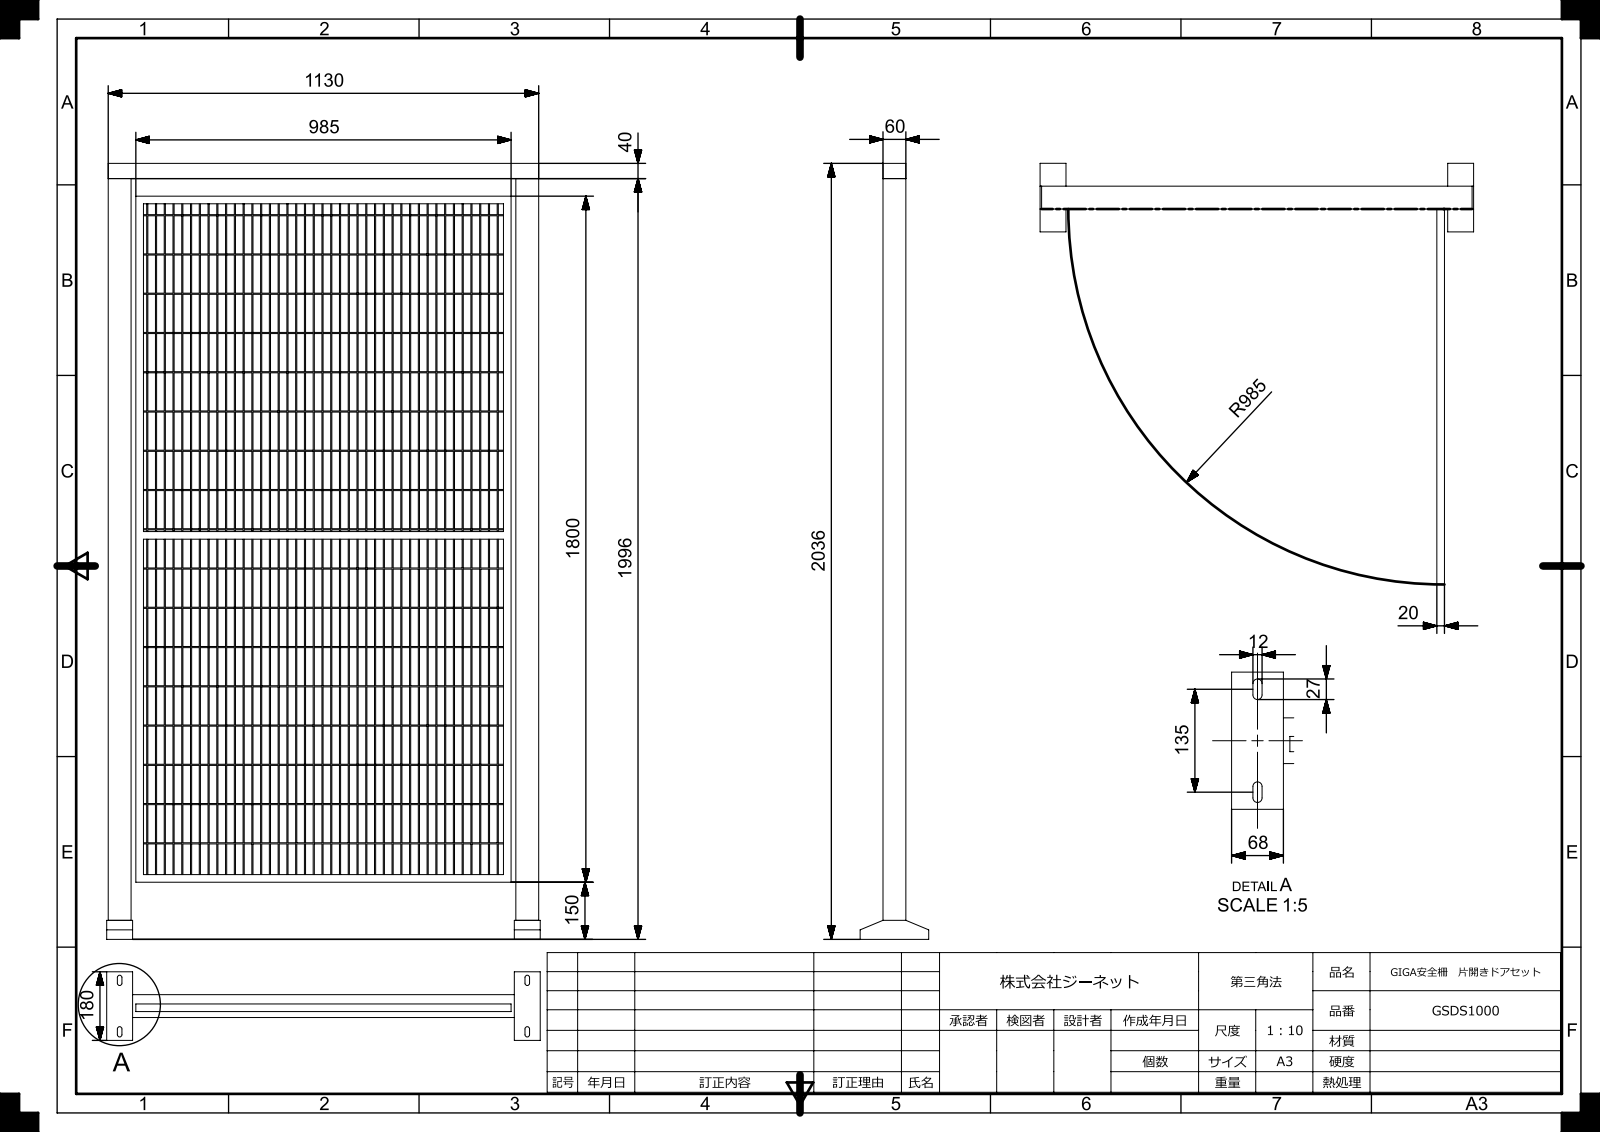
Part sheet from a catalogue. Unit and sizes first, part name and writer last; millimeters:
Units: millimetres
Overall size (bounding box): 2036 × 1138 × 180
Round bosses / shafts (diameter × count): ⌀3 ×58
Partial cylindrical surfaces — rounded edges, fillets, slot ends (radius × count): R6 ×8
Main face-to-face distances: 60, 20, 1070, 44.39, 15.61, 24.39, 35.61, 1130, 1010, 72.5
Volume: 20 940 000 mm³ · Surface area: 2 613 000 mm²
Bodies: 62 solids, 240 faces (172 planar, 68 cylindrical, 0 other)
Part name (STEP PRODUCT): top1; GSDS1000_post; GSDS1000_1; GSDS1000_202105
STEP written by: SIEMENS PLM Software NX 12.0 (AUTOMOTIVE_DESIGN)
